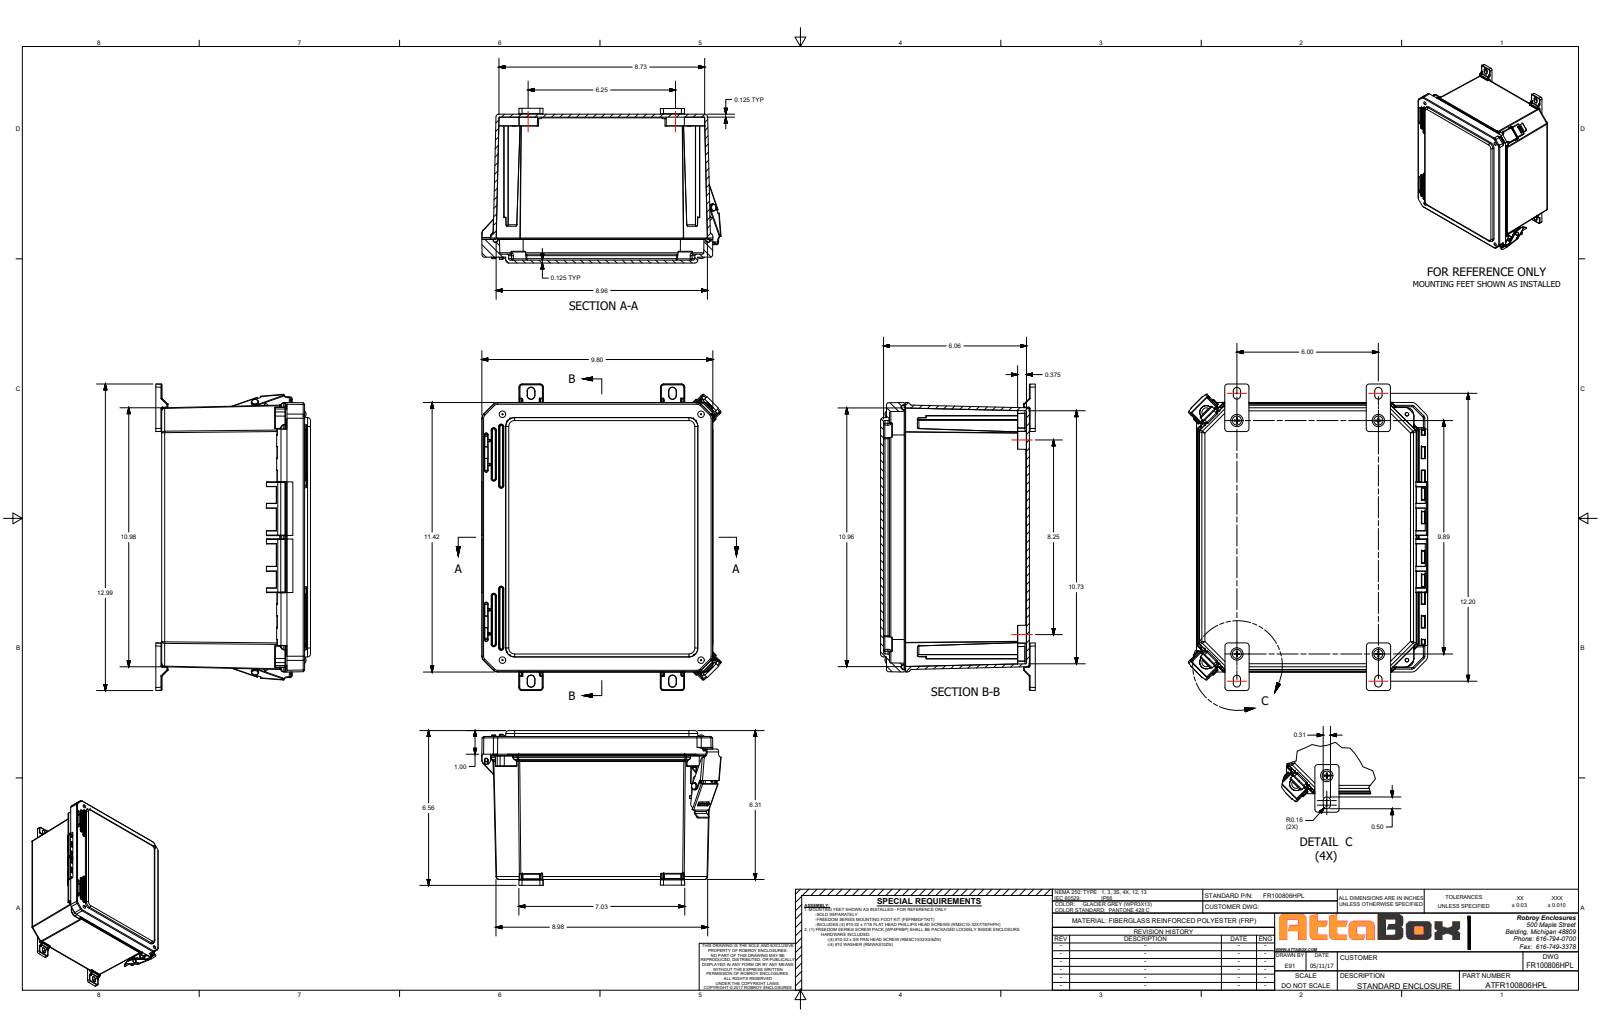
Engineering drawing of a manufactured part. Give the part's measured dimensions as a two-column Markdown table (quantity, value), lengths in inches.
| quantity | value |
| --- | --- |
| part name | FR100806HPL |
| STEP written by | SolidWorks 2021 (AUTOMOTIVE_DESIGN) |
| units | inches |
| bodies | 29 solids, 2380 faces (747 planar, 1029 cylindrical, 604 other) |
| overall size | 12.112 × 10.142 × 6.597 |
| volume | 70.85 in³ |
| surface area | 1 007 in² |
| round holes (diameter × count) | 0.135 × 8, 0.152 × 8, 0.159 × 8, 0.135 × 5, 0.15 × 4, 0.156 × 4, 0.252 × 4, 0.253 × 4, 0.137 × 3, 0.219 × 2, 0.227 × 2, 0.313 × 2 |
| round bosses / shafts (diameter × count) | 0.27 × 8, 0.87 × 4, 0.3 × 4, 0.262 × 4, 0.209 × 4, 0.135 × 4, 0.435 × 1, 0.435 × 1 |
| partial cylindrical surfaces (radius × count) | 0.01 × 174, 0.005 × 94, 0.02 × 70, 0.03 × 69, 0.06 × 36, 0.09 × 26, 0.03 × 24, 0.063 × 24 |
| main face-to-face distances | 0.125, 6.183, 6.059, 0.127, 6.308, 0.125, 0.126, 0.25, 5.934, 0.25 |
| hole center spacings | 9.399, 10.423, 9.776, 10.229, 7.415, 1.239, 1.536, 8.421 |
